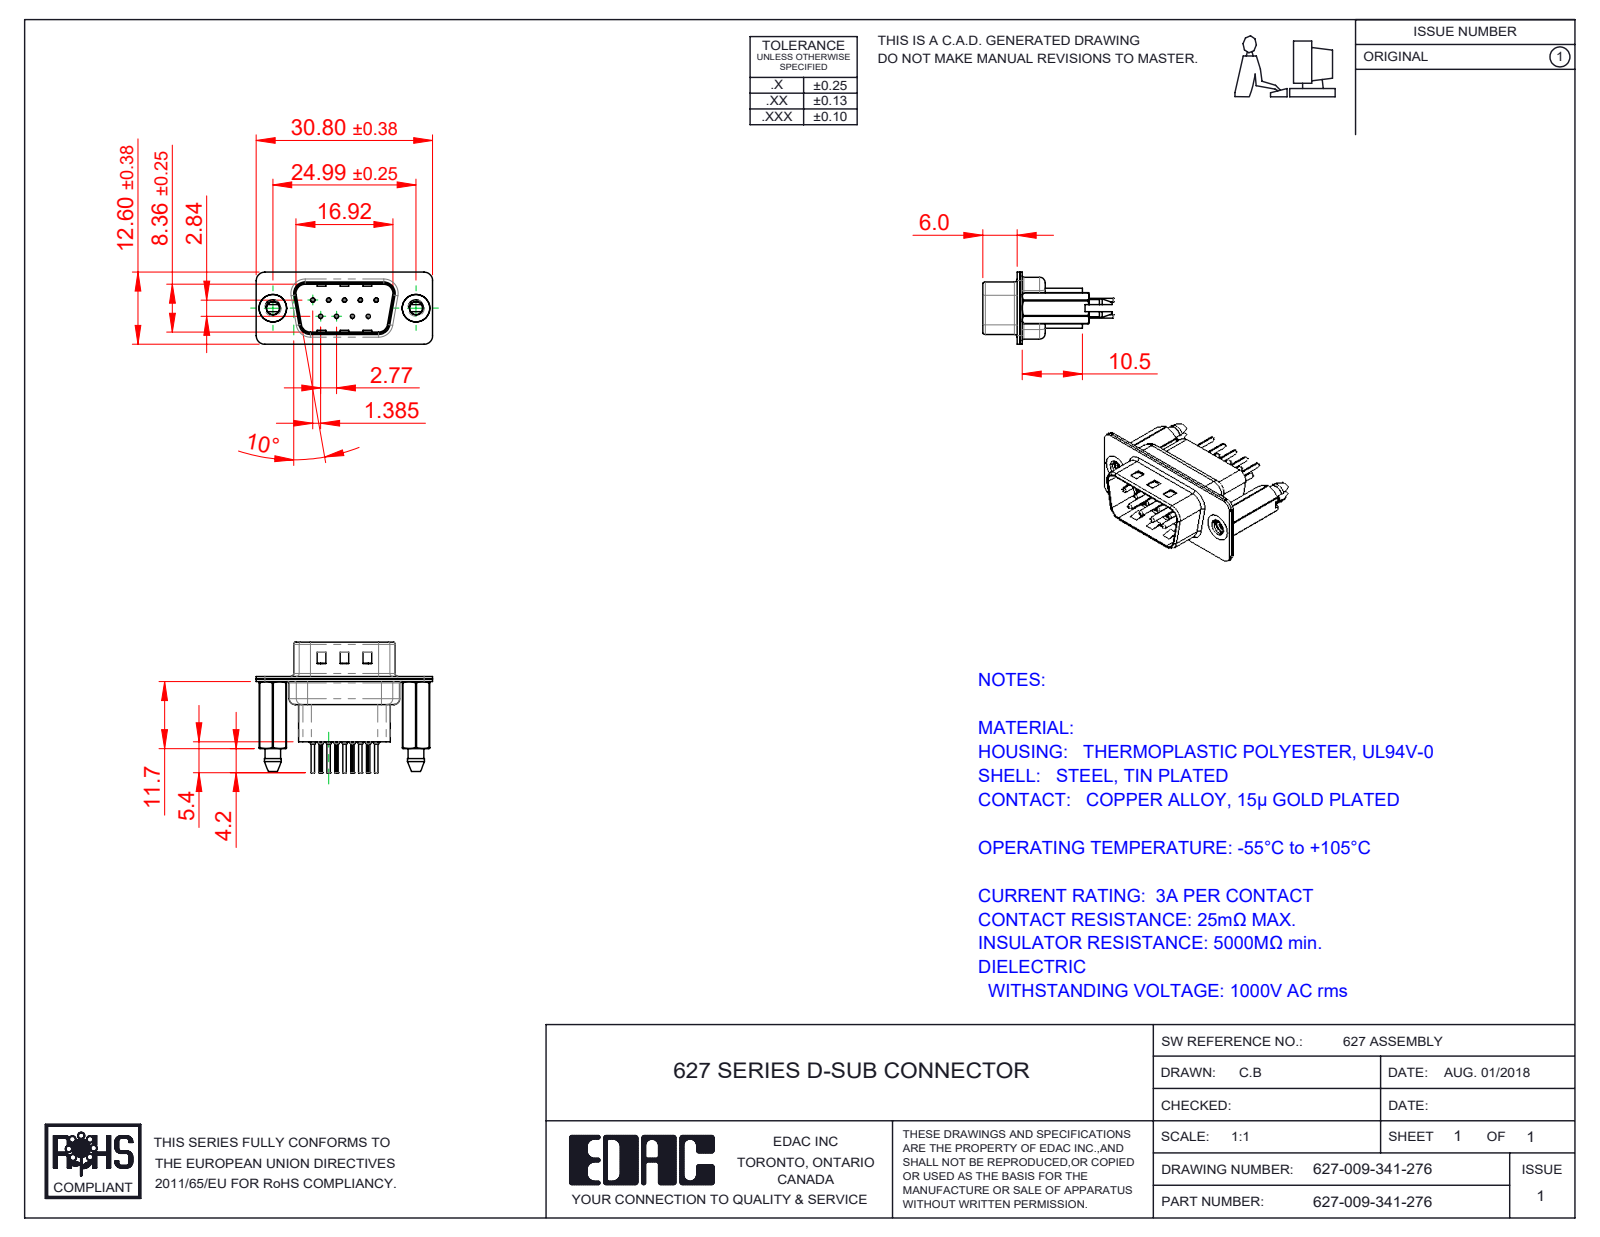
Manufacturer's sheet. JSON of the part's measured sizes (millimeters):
{"part_name": "627 Shell Front_09 Contacts; 627-009-341-076; 627 4-40 Threaded Boardlock_HP41; 627 Shell Rear_09 Contacts (+3 more)", "step_written_by": "SolidWorks 2020 (CONFIG_CONTROL_DESIGN)", "units": "millimeters", "bodies": {"solids": 14, "faces": 1294, "planar": 355, "cylindrical": 528, "other": 411}, "overall_size": [30.8, 22.8, 12.6], "volume_mm3": 2056, "surface_area_mm2": 5376, "round_holes": [[0.2, 9], [0.35, 9], [1.1, 9], [1.6, 9], [2.26, 2], [4, 2], [4.8, 2]], "round_bosses_or_shafts": [[2, 9], [1.5, 9], [0.75, 9], [0.6, 9], [4.9, 2]], "partial_cylinders_radius": [[1.5, 20], [0.1, 18], [2, 12], [1.6, 10], [0.5, 8], [0.25, 4], [0.6, 4], [0.65, 4]], "face_to_face_distances": [0.45, 0.4, 0.9, 0.82, 9.58, 1.4, 1.5, 0.68, 7.68, 4.76], "hole_center_spacings": [3.16, 2.77, 5.54, 5.03, 5.04, 8.31, 7.48, 7.49]}
